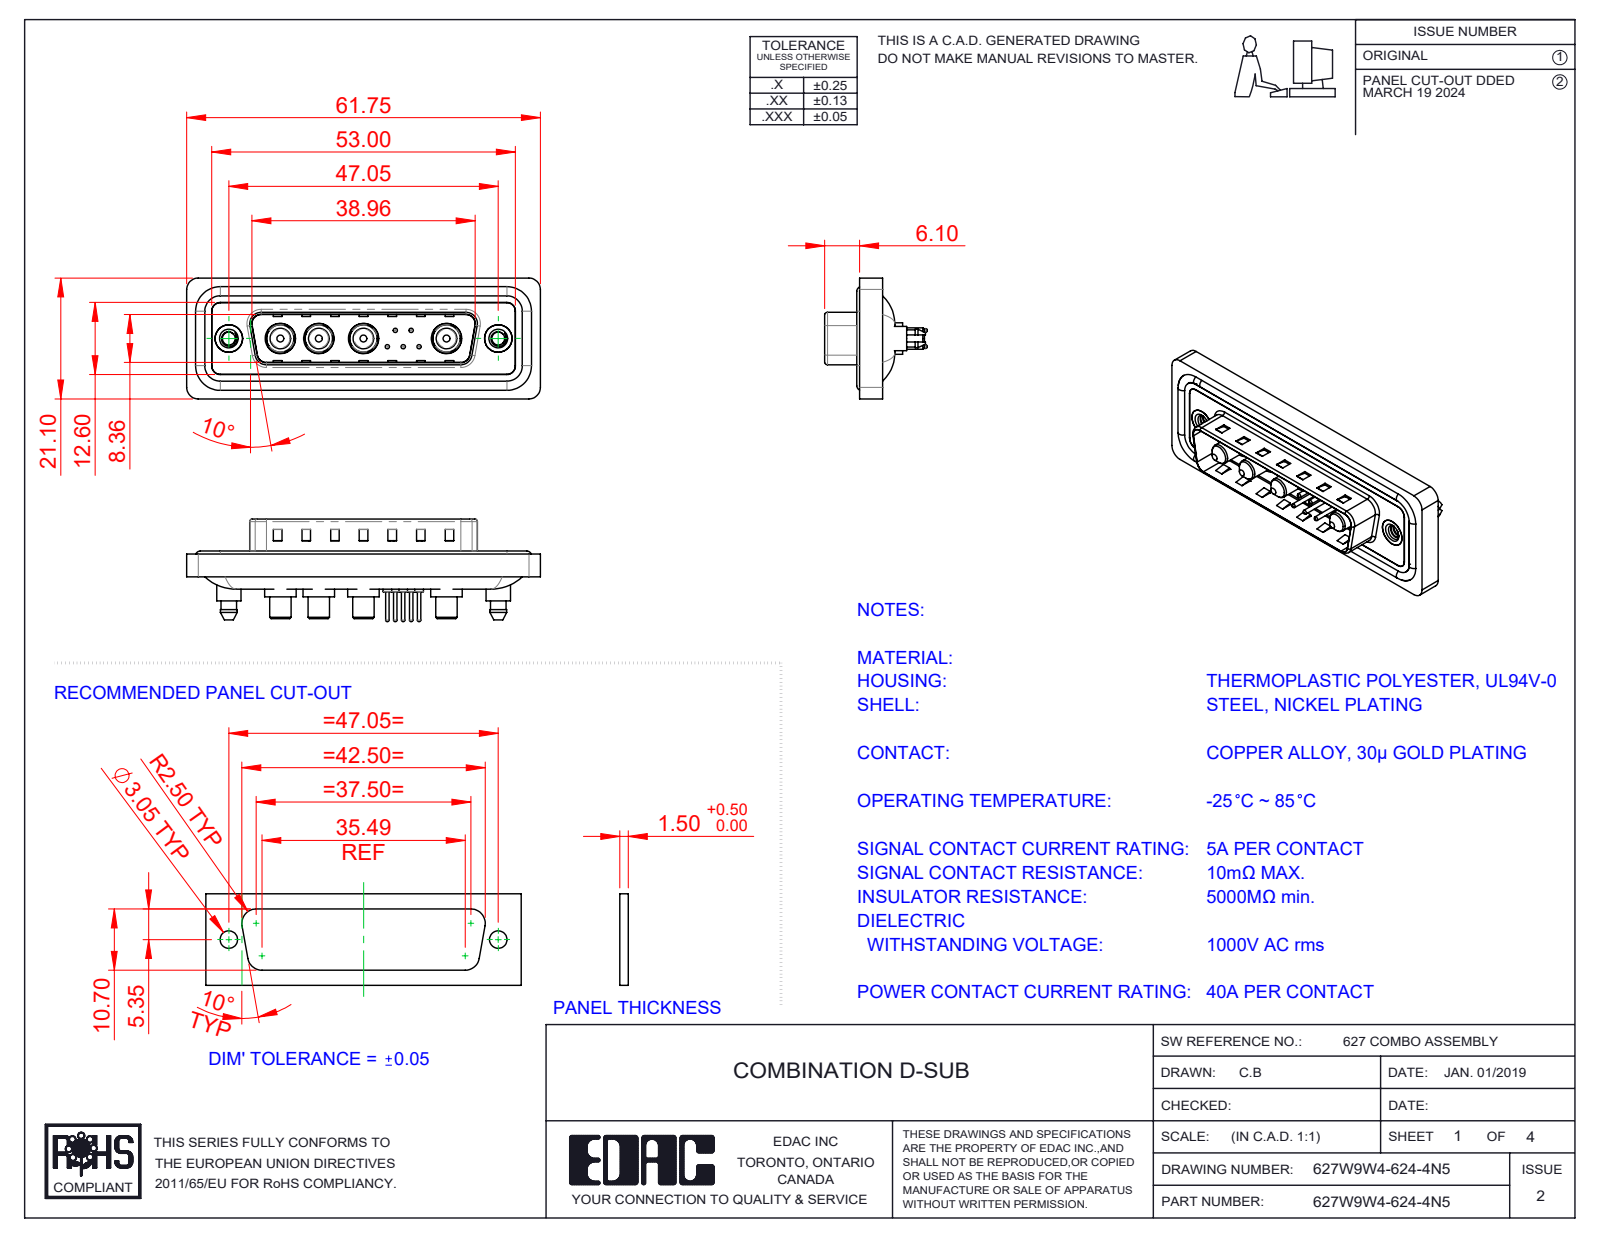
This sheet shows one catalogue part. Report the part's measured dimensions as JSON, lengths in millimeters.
{"part_name": "627Combo Shell Front_25 Contacts; 627Combo Contact Row 1_24; 627Combo Shell Rear_25 Contacts; 627W9W4-624-4N5 (+5 more)", "step_written_by": "SolidWorks 2023 (CONFIG_CONTROL_DESIGN)", "units": "millimeters", "bodies": {"solids": 20, "faces": 874, "planar": 300, "cylindrical": 366, "other": 208}, "overall_size": [61.75, 21.1, 17.9], "volume_mm3": 7612, "surface_area_mm2": 12212, "round_holes": [[0.75, 5], [1.6, 5], [2, 5], [4.85, 4], [5.3, 4], [2.26, 2], [4, 2], [4.8, 2], [5, 2]], "round_bosses_or_shafts": [[1.5, 5], [0.6, 5], [5.5, 4], [5.2, 4], [4.75, 4], [3.75, 4], [3.6, 4], [1.6, 4]], "partial_cylinders_radius": [[1.5, 24], [2, 18], [1.6, 10], [0.5, 8], [0.25, 4], [0.6, 4], [0.65, 4], [0.9, 4]], "face_to_face_distances": [0.4, 1.5, 1.1, 0.5, 3.1, 1.6, 2.9, 0.82, 9.58, 5.65], "hole_center_spacings": [3.16, 2.77, 5.04, 14.51, 2.78, 4.4, 4.41, 5]}
